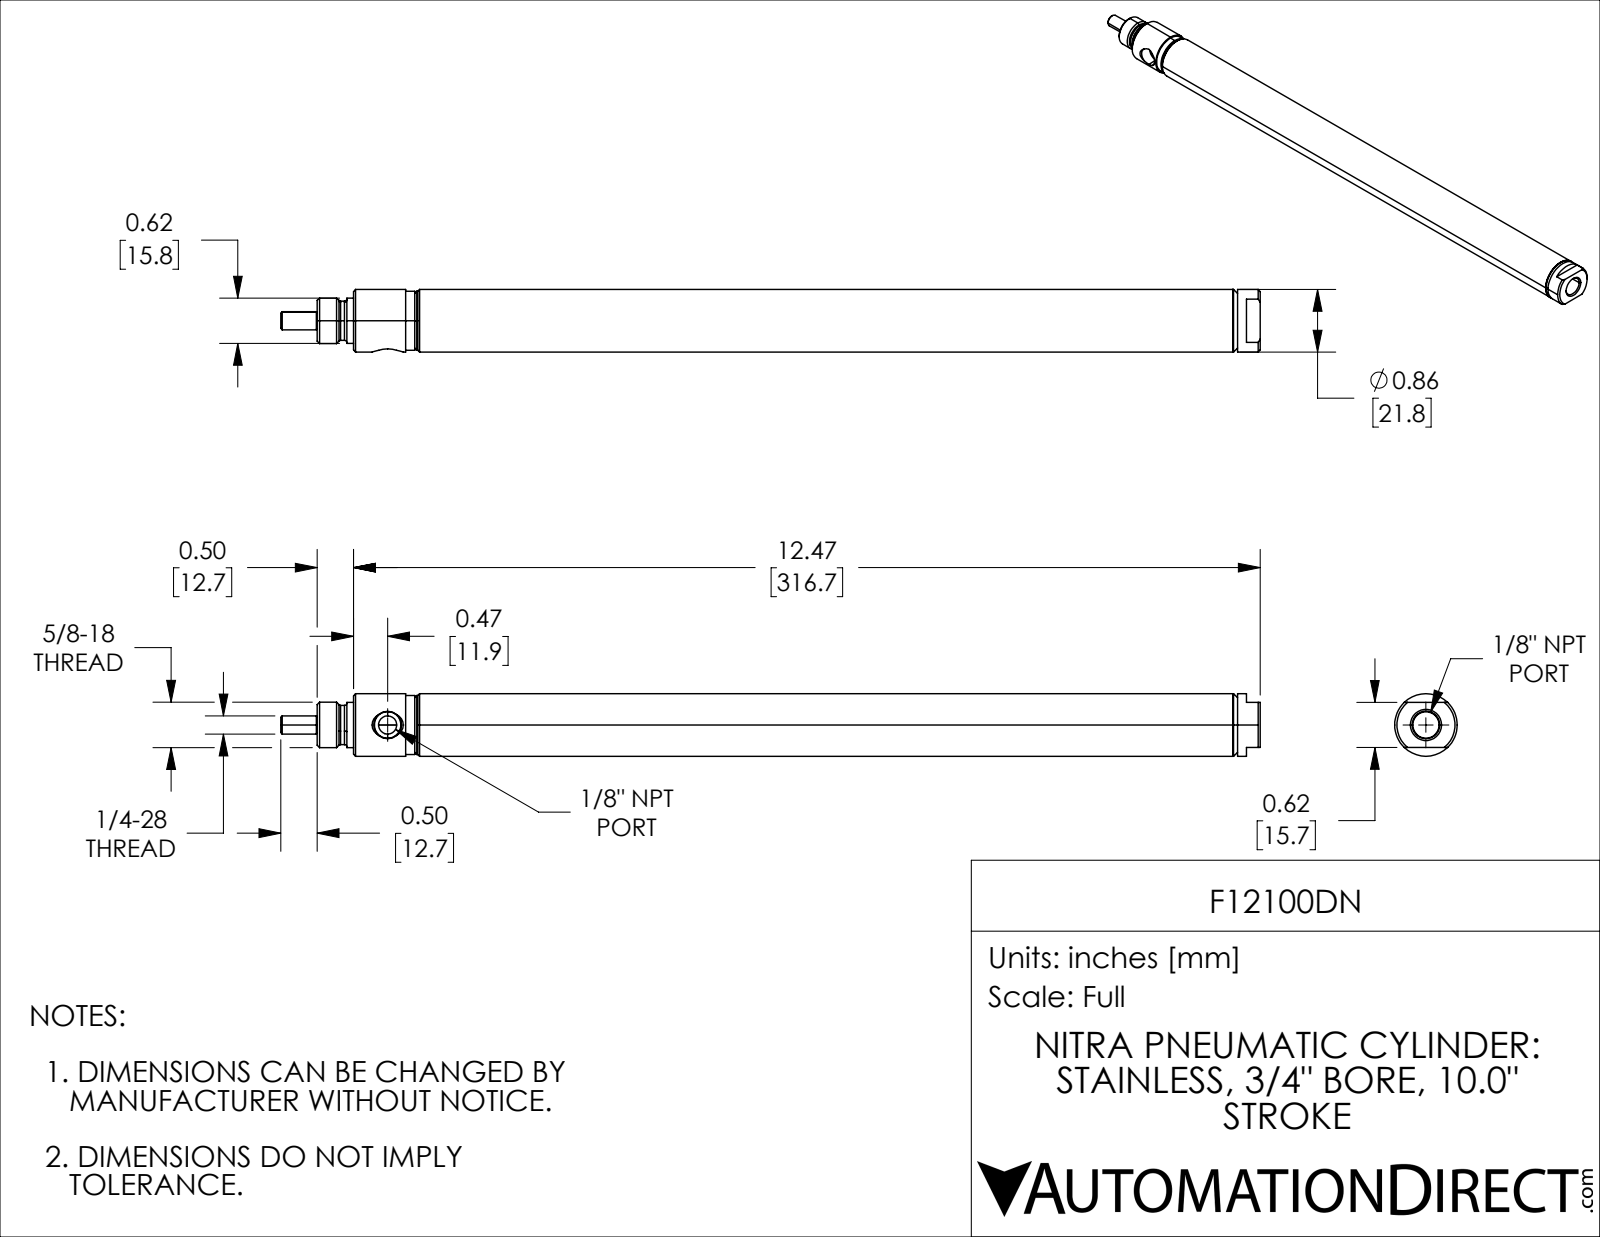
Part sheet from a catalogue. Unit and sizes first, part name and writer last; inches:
Units: inches
Overall size (bounding box): 13.469 × 0.86 × 0.86
Round holes (diameter × count): ⌀0.25 ×1, ⌀0.274 ×1, ⌀0.5 ×1, ⌀0.702 ×1
Round bosses / shafts (diameter × count): ⌀0.86 ×1, ⌀0.81 ×1, ⌀0.762 ×1, ⌀0.625 ×1, ⌀0.622 ×1, ⌀0.539 ×1, ⌀0.25 ×1, ⌀0.23 ×1
Main face-to-face distances: 0.844, 10, 10.844, 11.375, 1.375, 0.531, 0.5, 1.094, 11.094, 11.938
Volume: 3.175 in³ · Surface area: 80.39 in²
Bodies: 4 solids, 124 faces (22 planar, 46 cylindrical, 56 other)
Part name (STEP PRODUCT): F12100DN; F12100DN_5; F12100DN_9; F12100DN_7 (+1 more)
STEP written by: SolidWorks 2021 (CONFIG_CONTROL_DESIGN)
